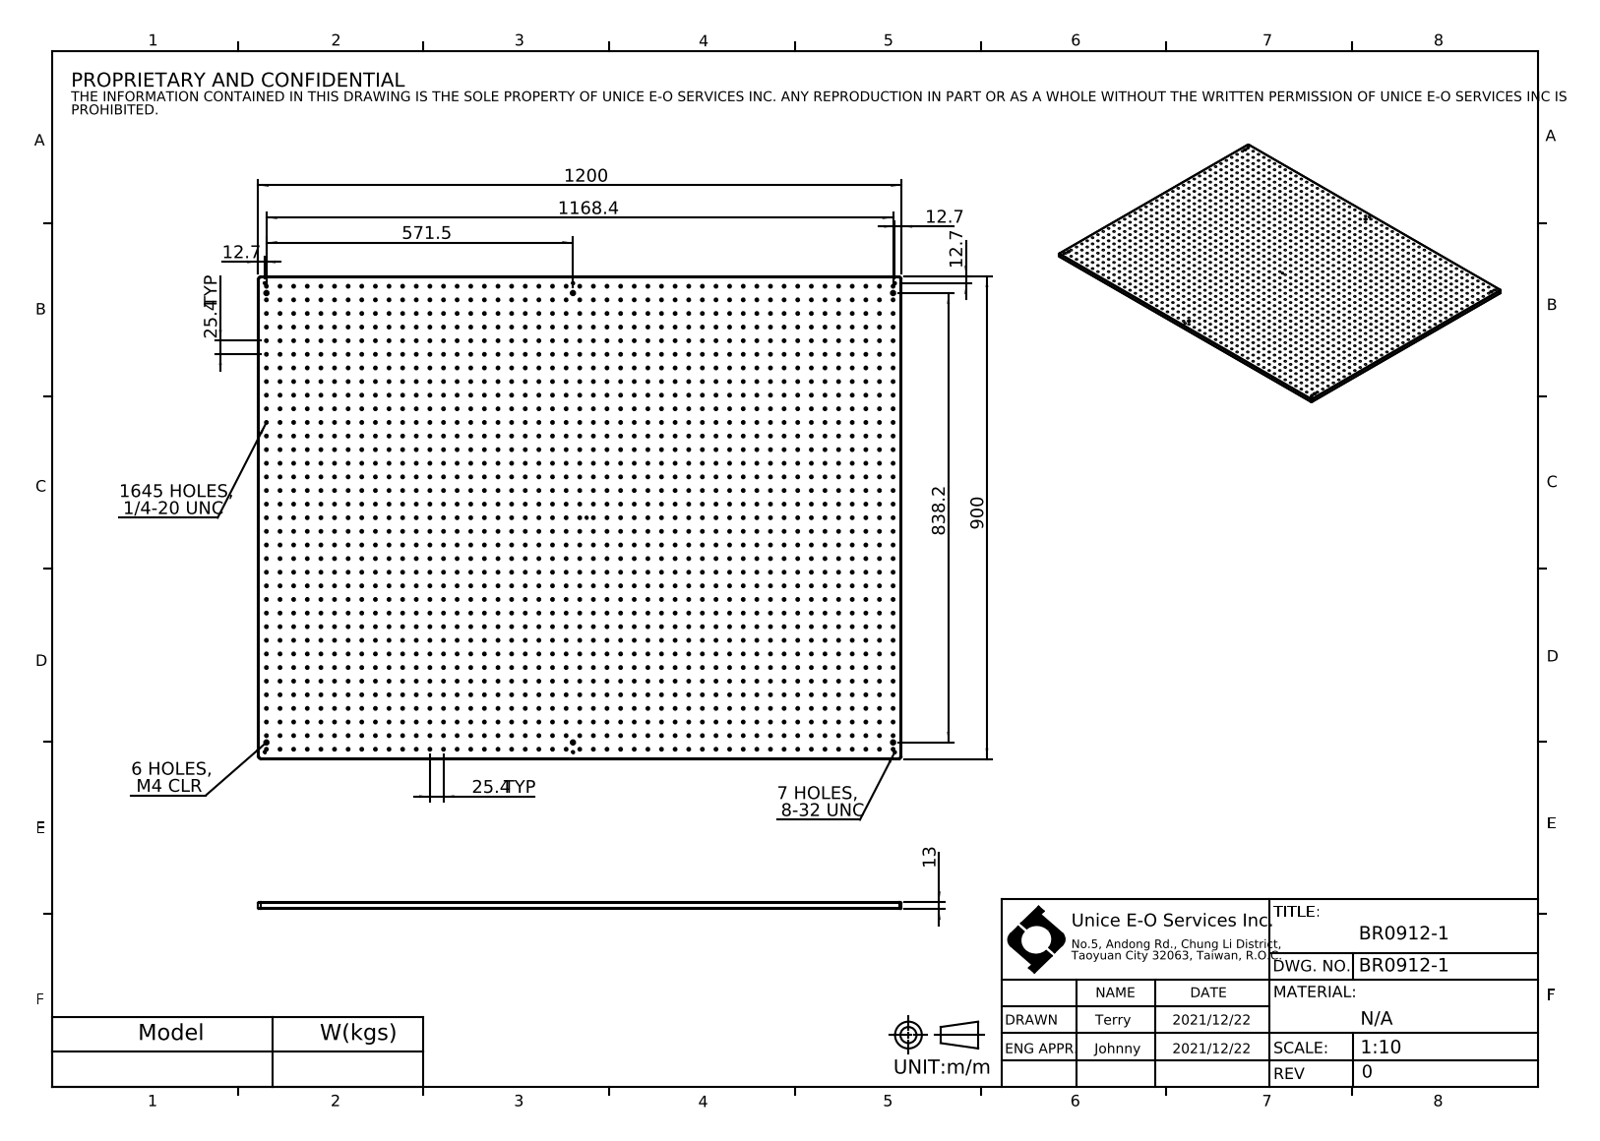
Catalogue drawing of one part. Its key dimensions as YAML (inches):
part_name: "BR0912-1"
step_written_by: "SolidWorks 2021 (CONFIG_CONTROL_DESIGN)"
units: inches
bodies: {solids: 1, faces: 3360, planar: 12, cylindrical: 3340, other: 8}
overall_size: [47.244, 35.433, 0.512]
volume: 829.3
surface_area: 3852
round_holes:
  - {diameter: 0.201, count: 1645}
  - {diameter: 0.136, count: 7}
  - {diameter: 0.177, count: 6}
  - {diameter: 0.315, count: 6}
partial_cylinders:
  - {radius: 0.079, count: 8}
  - {radius: 0.197, count: 4}
face_to_face_distances: [0.512, 35.433, 47.244, 0.339, 0.173]
hole_center_spacings: [1, 2, 3, 4, 5, 6, 7, 8]
